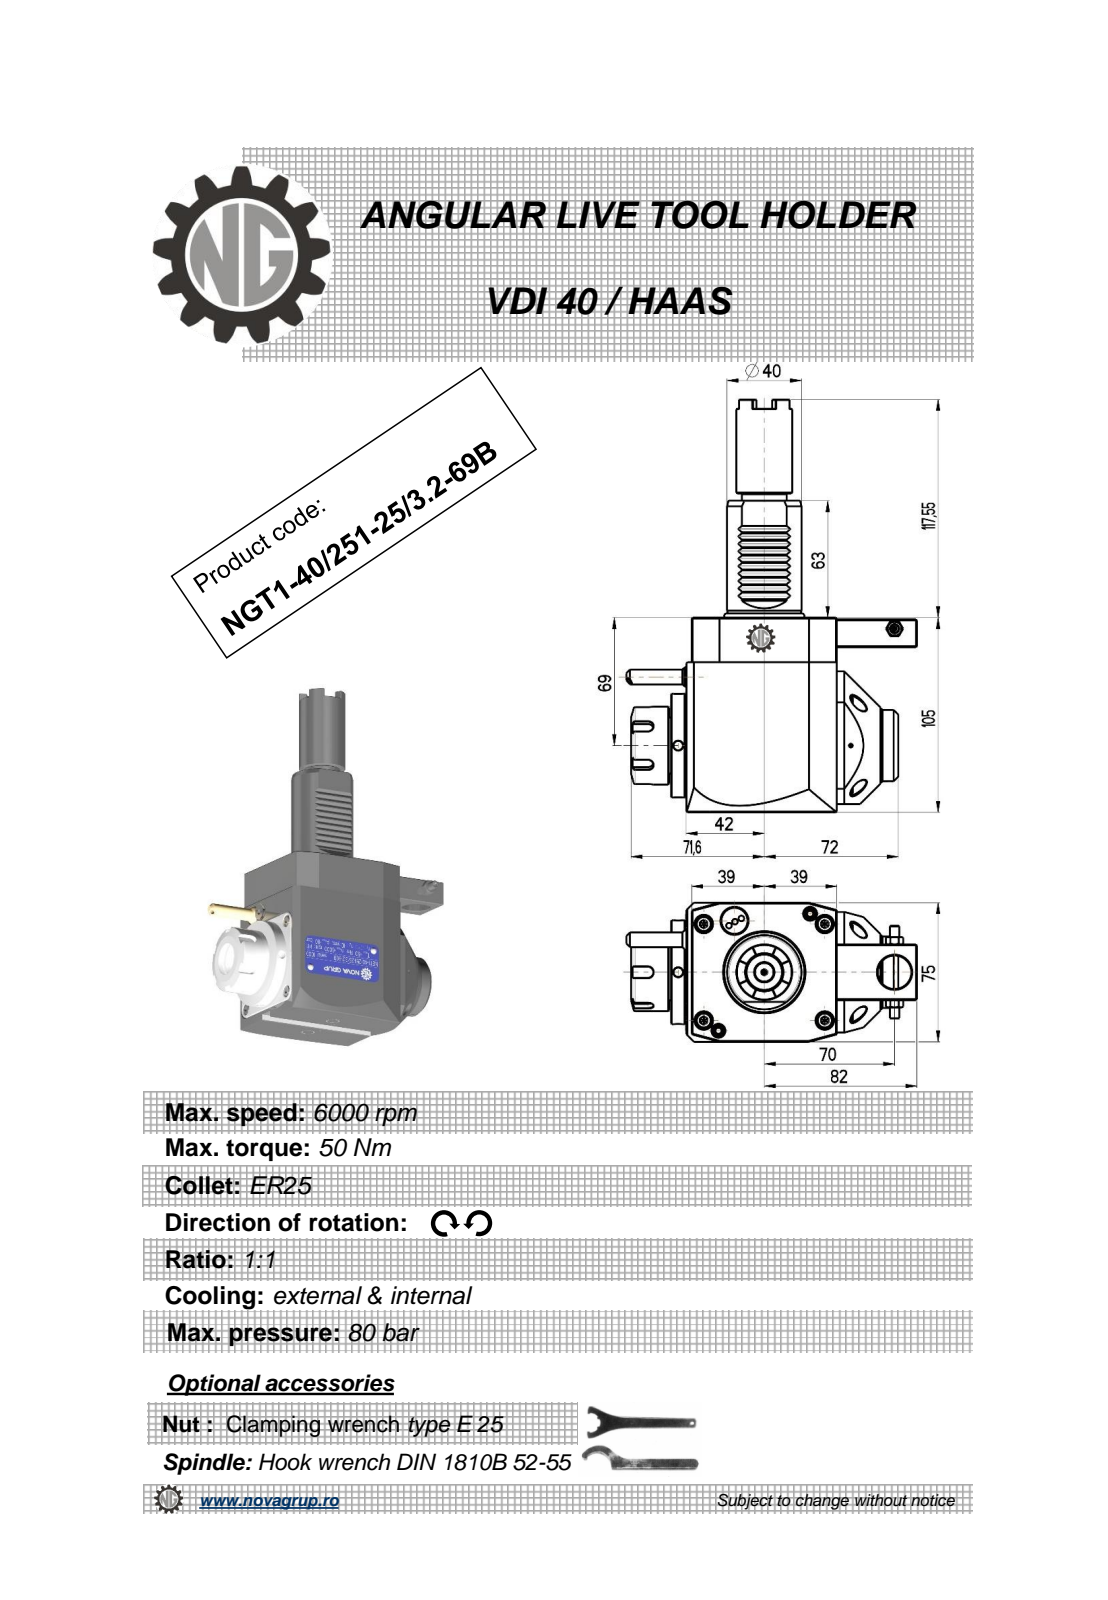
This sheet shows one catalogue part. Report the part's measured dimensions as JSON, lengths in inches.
{"part_name": "NGT1_40_251_25_3_2_69B", "step_written_by": "PRO/ENGINEER BY PARAMETRIC TECHNOLOGY CORPORATION, 2010280 (CONFIG_CONTROL_DESIGN)", "units": "inches", "bodies": {"solids": 1, "faces": 465, "planar": 216, "cylindrical": 91, "other": 158}, "overall_size": [8.762, 6.147, 2.953], "volume_in3": 53.2, "surface_area_in2": 117.1, "round_holes": [[0.197, 3], [0.118, 1], [0.165, 1], [0.374, 1], [0.709, 1], [0.799, 1]], "round_bosses_or_shafts": [[2.205, 1], [1.693, 1], [1.654, 1], [1.575, 1], [1.516, 1], [1.299, 1], [1.181, 1], [0.945, 1]], "partial_cylinders_radius": [[0.01, 12], [0.012, 10], [0.008, 6], [0.118, 5], [0.02, 1], [0.394, 1], [1.575, 1]], "face_to_face_distances": [2.953, 4.134, 3.504, 3.189, 0.315, 0.433, 0.039, 0.118, 0.11, 3.071], "hole_center_spacings": [1.185, 1.611, 2.421, 4.577, 5.206]}
